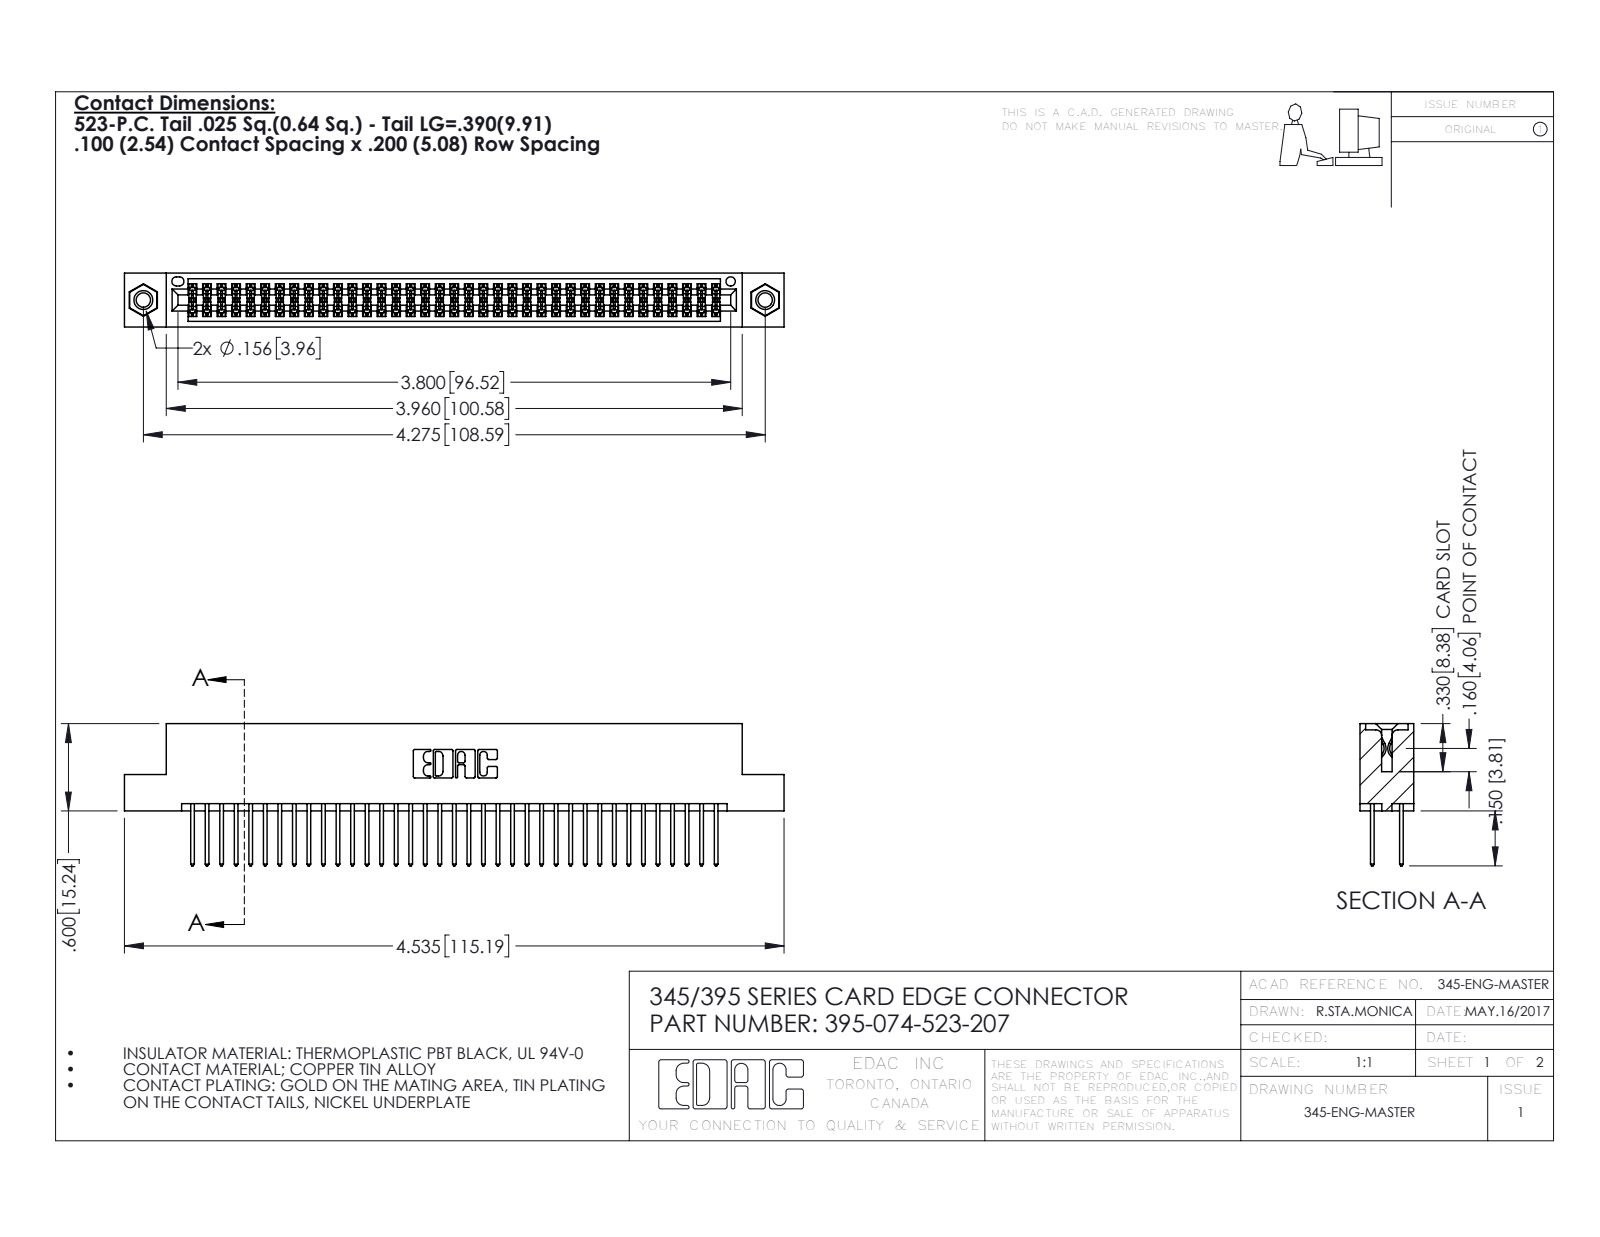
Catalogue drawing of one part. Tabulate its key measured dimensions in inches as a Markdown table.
| quantity | value |
| --- | --- |
| part name | 345-250-001_345-250-005-103; 345-292-001_345-293-123; 345 Part_Flush Mounting Lugs - 0.156 Dia-TI; 395-074-523-207 |
| STEP written by | SolidWorks 2016 (CONFIG_CONTROL_DESIGN) |
| units | inches |
| bodies | 77 solids, 3886 faces (2554 planar, 1316 cylindrical, 16 other) |
| overall size | 4.535 × 0.977 × 0.37 |
| volume | 0.688 in³ |
| surface area | 26.8 in² |
| round holes (diameter × count) | 0.098 × 2, 0.125 × 2, 0.156 × 2, 0.064 × 1 |
| round bosses / shafts (diameter × count) | 0.155 × 2 |
| partial cylindrical surfaces (radius × count) | 0.006 × 111, 0.01 × 74, 0.01 × 22, 0.007 × 6, 0.031 × 6, 0.026 × 3, 0.014 × 2, 0.019 × 2 |
| main face-to-face distances | 0.072, 0.298, 0.2, 0.098, 0.272, 0.025, 0.37, 0.225, 0.175, 0.149 |
| hole center spacings | 0.27, 4.039, 4.275 |
